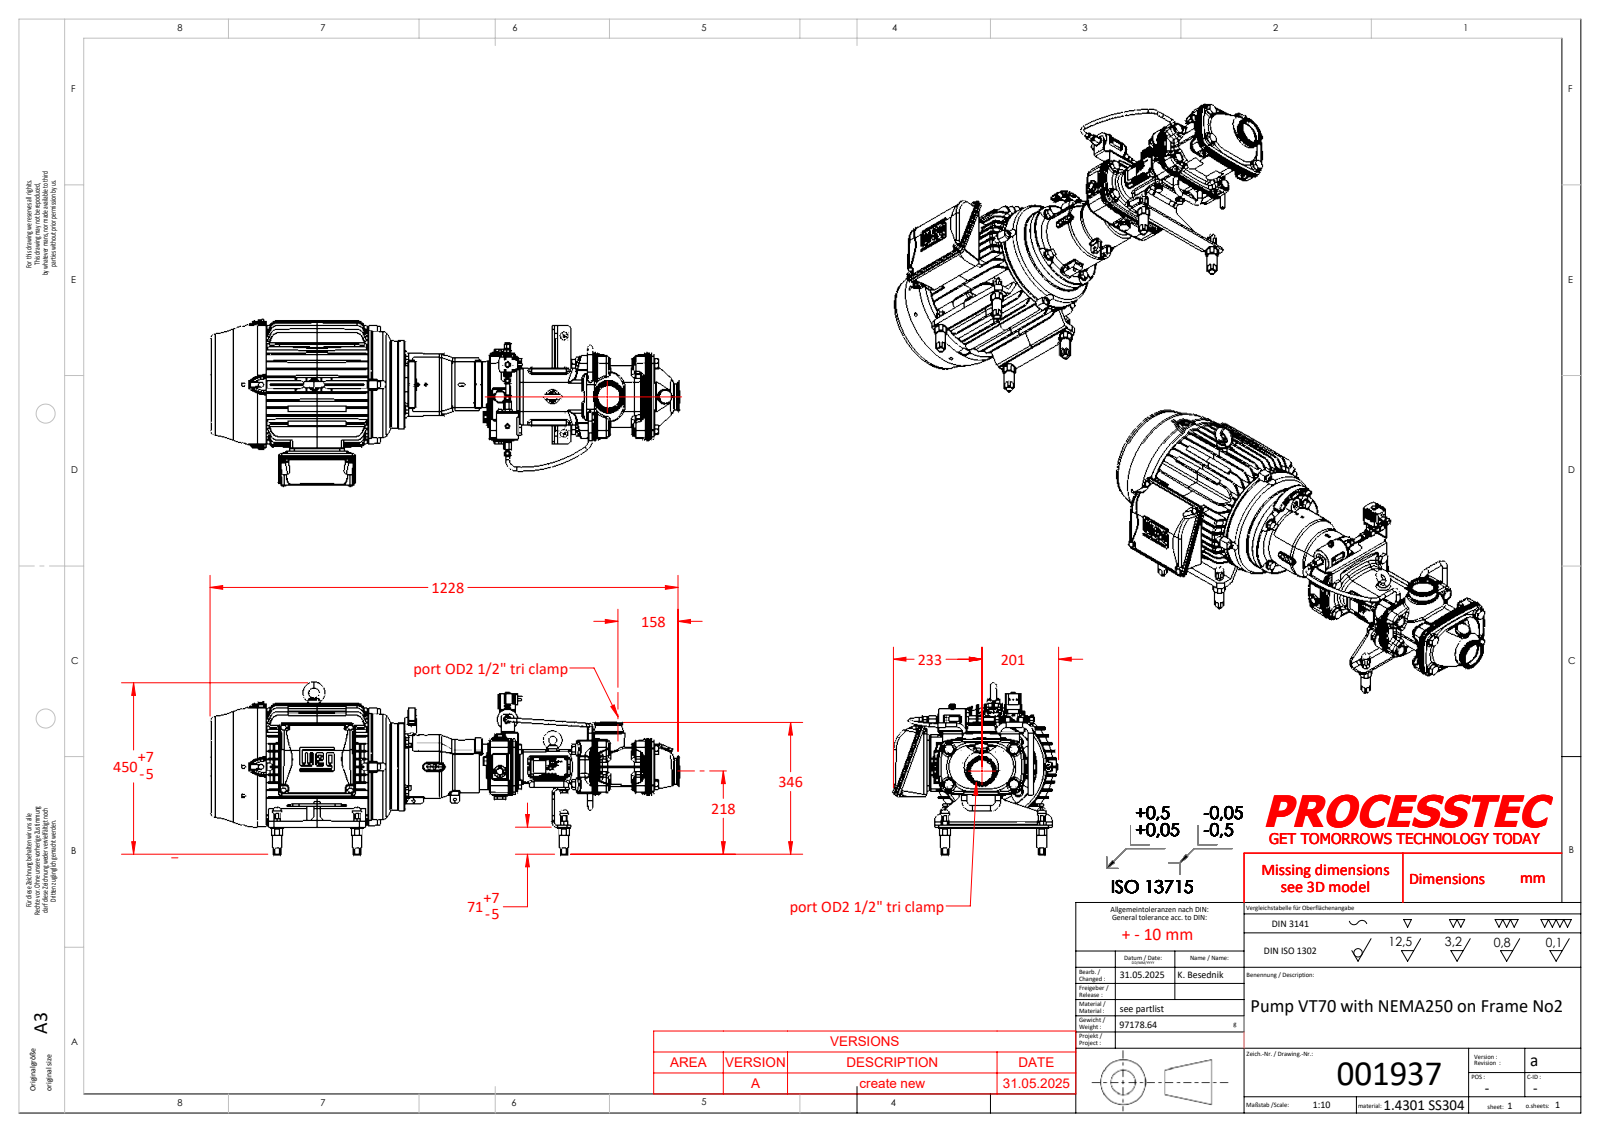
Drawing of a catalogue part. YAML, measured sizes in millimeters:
part_name: "001938_6 mm; 001583; 001067_ISO 4029 - M10 X 20; 001115_ISO 4029 - M8 X 20 (+8 more)"
step_written_by: "SolidWorks 2023 (AUTOMOTIVE_DESIGN)"
units: millimeters
bodies: {solids: 138, faces: 13438, planar: 5558, cylindrical: 2876, other: 5004}
overall_size: [1228.15, 449.75, 434.2]
volume: 51330000
surface_area: 3549000
round_holes:
  - {diameter: 8, count: 17}
  - {diameter: 14, count: 16}
  - {diameter: 8.5, count: 11}
  - {diameter: 10.2, count: 10}
  - {diameter: 12, count: 10}
  - {diameter: 6, count: 7}
  - {diameter: 5.9, count: 6}
  - {diameter: 7.2, count: 6}
  - {diameter: 22.2, count: 6}
  - {diameter: 2.5, count: 5}
  - {diameter: 7.5, count: 5}
  - {diameter: 17, count: 5}
round_bosses_or_shafts:
  - {diameter: 6, count: 27}
  - {diameter: 10, count: 12}
  - {diameter: 16, count: 11}
  - {diameter: 8, count: 9}
  - {diameter: 24, count: 8}
  - {diameter: 12, count: 8}
  - {diameter: 30, count: 7}
  - {diameter: 22, count: 7}
partial_cylinders:
  - {radius: 3, count: 231}
  - {radius: 2, count: 71}
  - {radius: 5, count: 44}
  - {radius: 8, count: 36}
  - {radius: 1.4, count: 32}
  - {radius: 1.2, count: 27}
  - {radius: 1.5, count: 25}
  - {radius: 4, count: 21}
face_to_face_distances: [19.8, 39.6, 265.9, 14, 5.8, 121.2, 141, 101.4, 33.8, 160.8]
hole_center_spacings: [130.23, 41, 108, 22.59, 45, 51.65, 65.5, 65.51]
